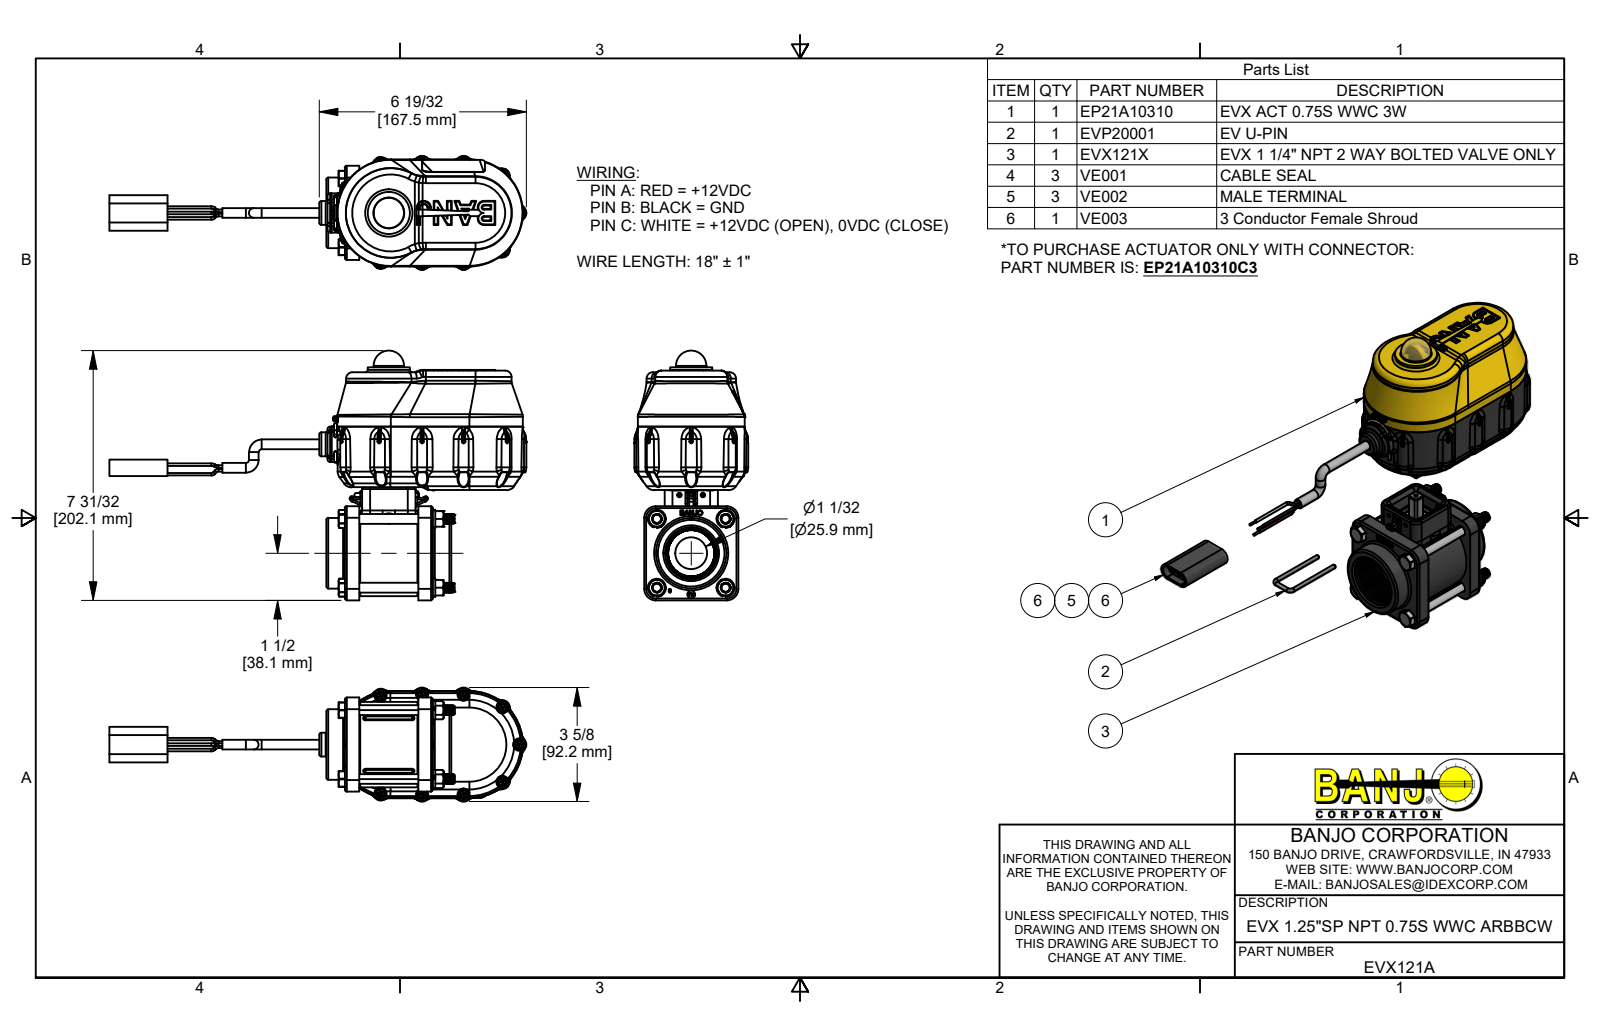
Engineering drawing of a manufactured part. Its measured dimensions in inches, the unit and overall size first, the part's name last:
Units: inches
Overall size (bounding box): 49.551 × 7.957 × 3.63
Round holes (diameter × count): ⌀0.095 ×11, ⌀0.15 ×11, ⌀0.08 ×7, ⌀0.15 ×7, ⌀0.25 ×5, ⌀0.107 ×4, ⌀0.126 ×4, ⌀0.135 ×4, ⌀0.136 ×4, ⌀0.148 ×4, ⌀0.17 ×4, ⌀0.252 ×4
Round bosses / shafts (diameter × count): ⌀0.268 ×60, ⌀0.08 ×18, ⌀0.25 ×17, ⌀0.14 ×11, ⌀0.108 ×11, ⌀0.085 ×11, ⌀0.058 ×6, ⌀0.313 ×5
Partial cylindrical surfaces — rounded edges, fillets, slot ends (radius × count): R0.013 ×180, R0.04 ×145, R0.01 ×84, R0.02 ×72, R0.06 ×58, R0.005 ×53, R0.03 ×38, R0.08 ×28
Main face-to-face distances: 0.1, 2.565, 0.211, 0.06, 0.151, 0.46, 2.345, 0.055, 0.125, 1.896
Hole centre spacings: 1.046, 1.55, 1.662, 1.891, 2.192, 2.656, 2.69, 2.715
Volume: 49.47 in³ · Surface area: 872.3 in²
Bodies: 103 solids, 11757 faces (3056 planar, 3496 cylindrical, 5205 other)
Part name (STEP PRODUCT): EVX121A; EP21A10310; EP10310; IRF4905 (+8 more)
STEP written by: Autodesk Inventor 2019 (AUTOMOTIVE_DESIGN)
